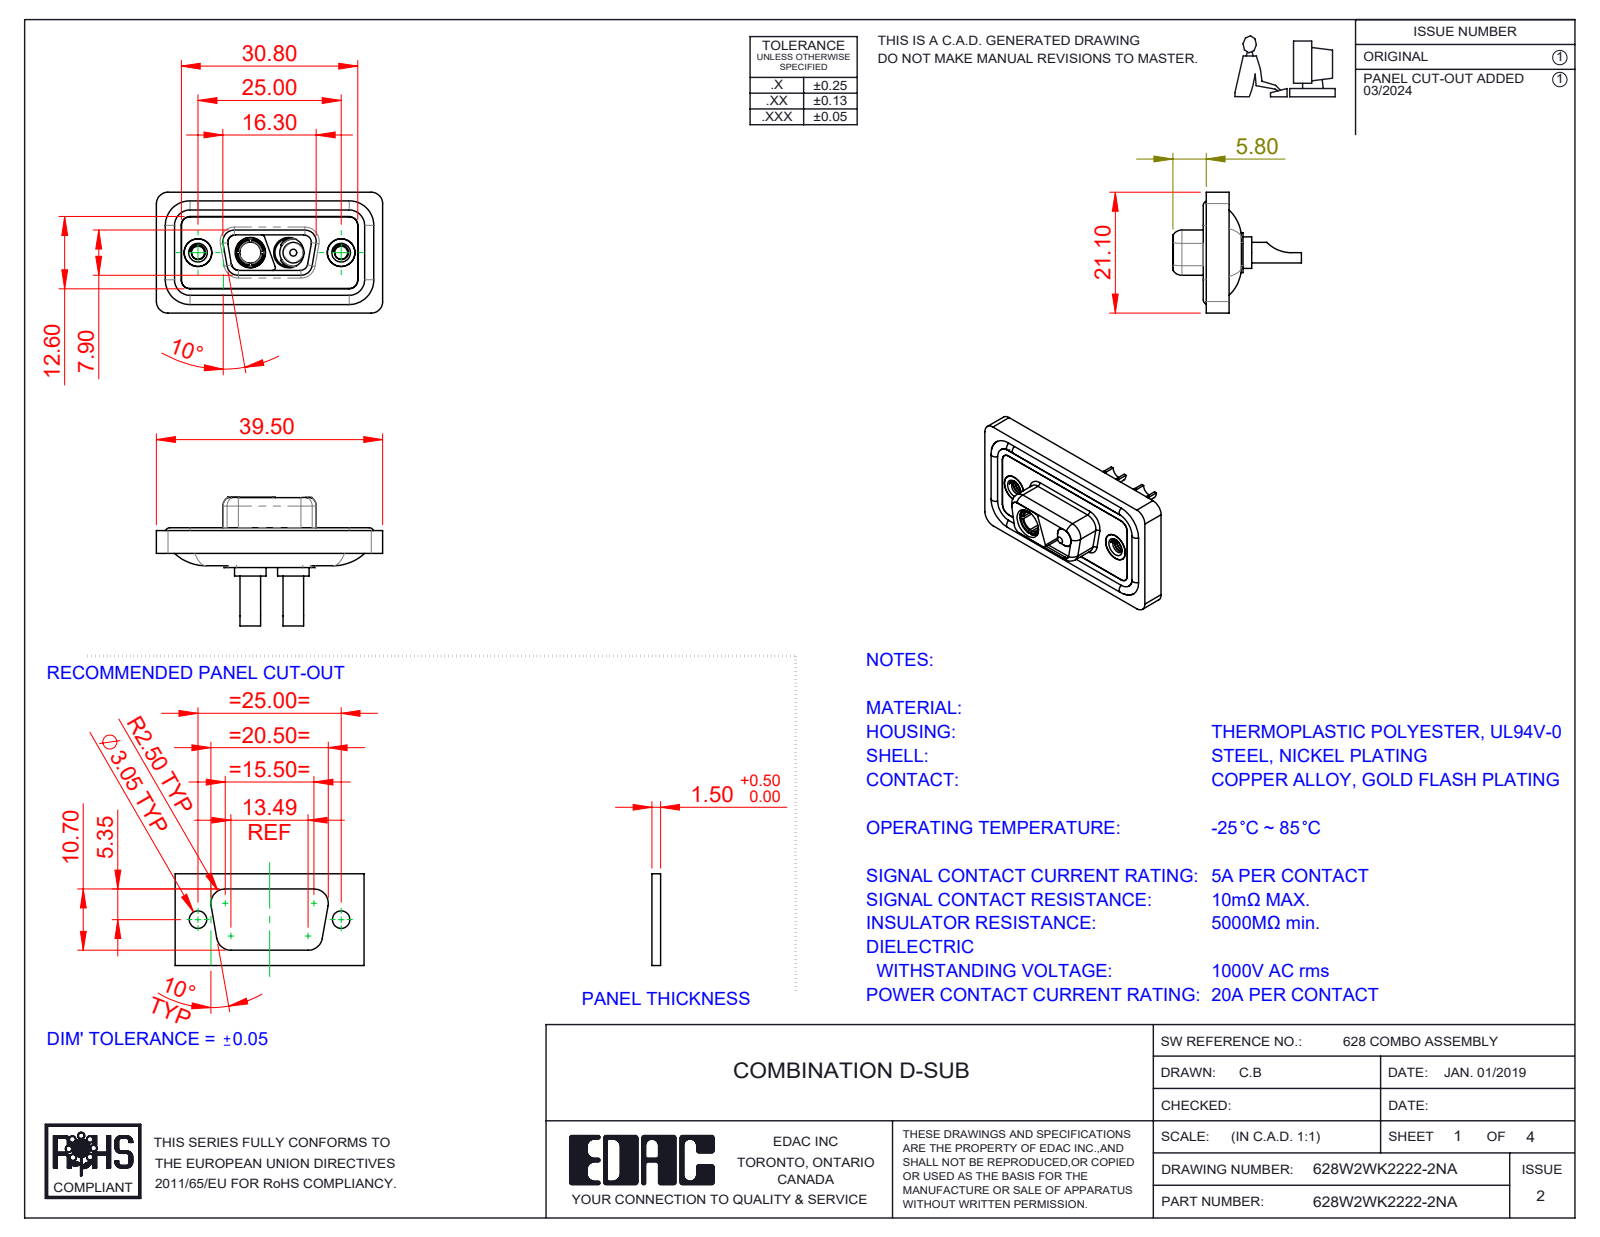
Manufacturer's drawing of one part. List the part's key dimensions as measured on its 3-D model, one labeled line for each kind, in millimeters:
Part name (STEP PRODUCT): 628Combo Shell Rear_09 Contacts; 628Combo Waterproof Housing_09 Contacts; 628Combo Threaded Rivet_A; 628W2WK2222-2NA (+4 more)
STEP written by: SolidWorks 2023 (CONFIG_CONTROL_DESIGN)
Units: millimetres
Bodies: 11 solids, 510 faces (150 planar, 239 cylindrical, 121 other)
Overall size (bounding box): 39.5 × 22.45 × 21.1
Volume: 4 630 mm³ · Surface area: 7 506 mm²
Round holes (diameter × count): ⌀4.85 ×4, ⌀2.26 ×2, ⌀2.7 ×2, ⌀4 ×2, ⌀4.05 ×2, ⌀5 ×2, ⌀5.3 ×2, ⌀3.7 ×1
Round bosses / shafts (diameter × count): ⌀1.6 ×4, ⌀5.5 ×2, ⌀5.2 ×2, ⌀4.95 ×2, ⌀4.8 ×2, ⌀4.75 ×2, ⌀3.75 ×2, ⌀3.6 ×2
Partial cylindrical surfaces — rounded edges, fillets, slot ends (radius × count): R1.5 ×22, R2 ×18, R1.35 ×8, R1.6 ×8, R0.5 ×6, R0.25 ×4, R0.6 ×4, R0.65 ×4
Main face-to-face distances: 0.4, 1.1, 2.9, 1.6, 0.5, 1.8, 5.65, 1.5, 5.35, 3.1
Hole centre spacings: 9.14, 15.86, 6.72, 25
